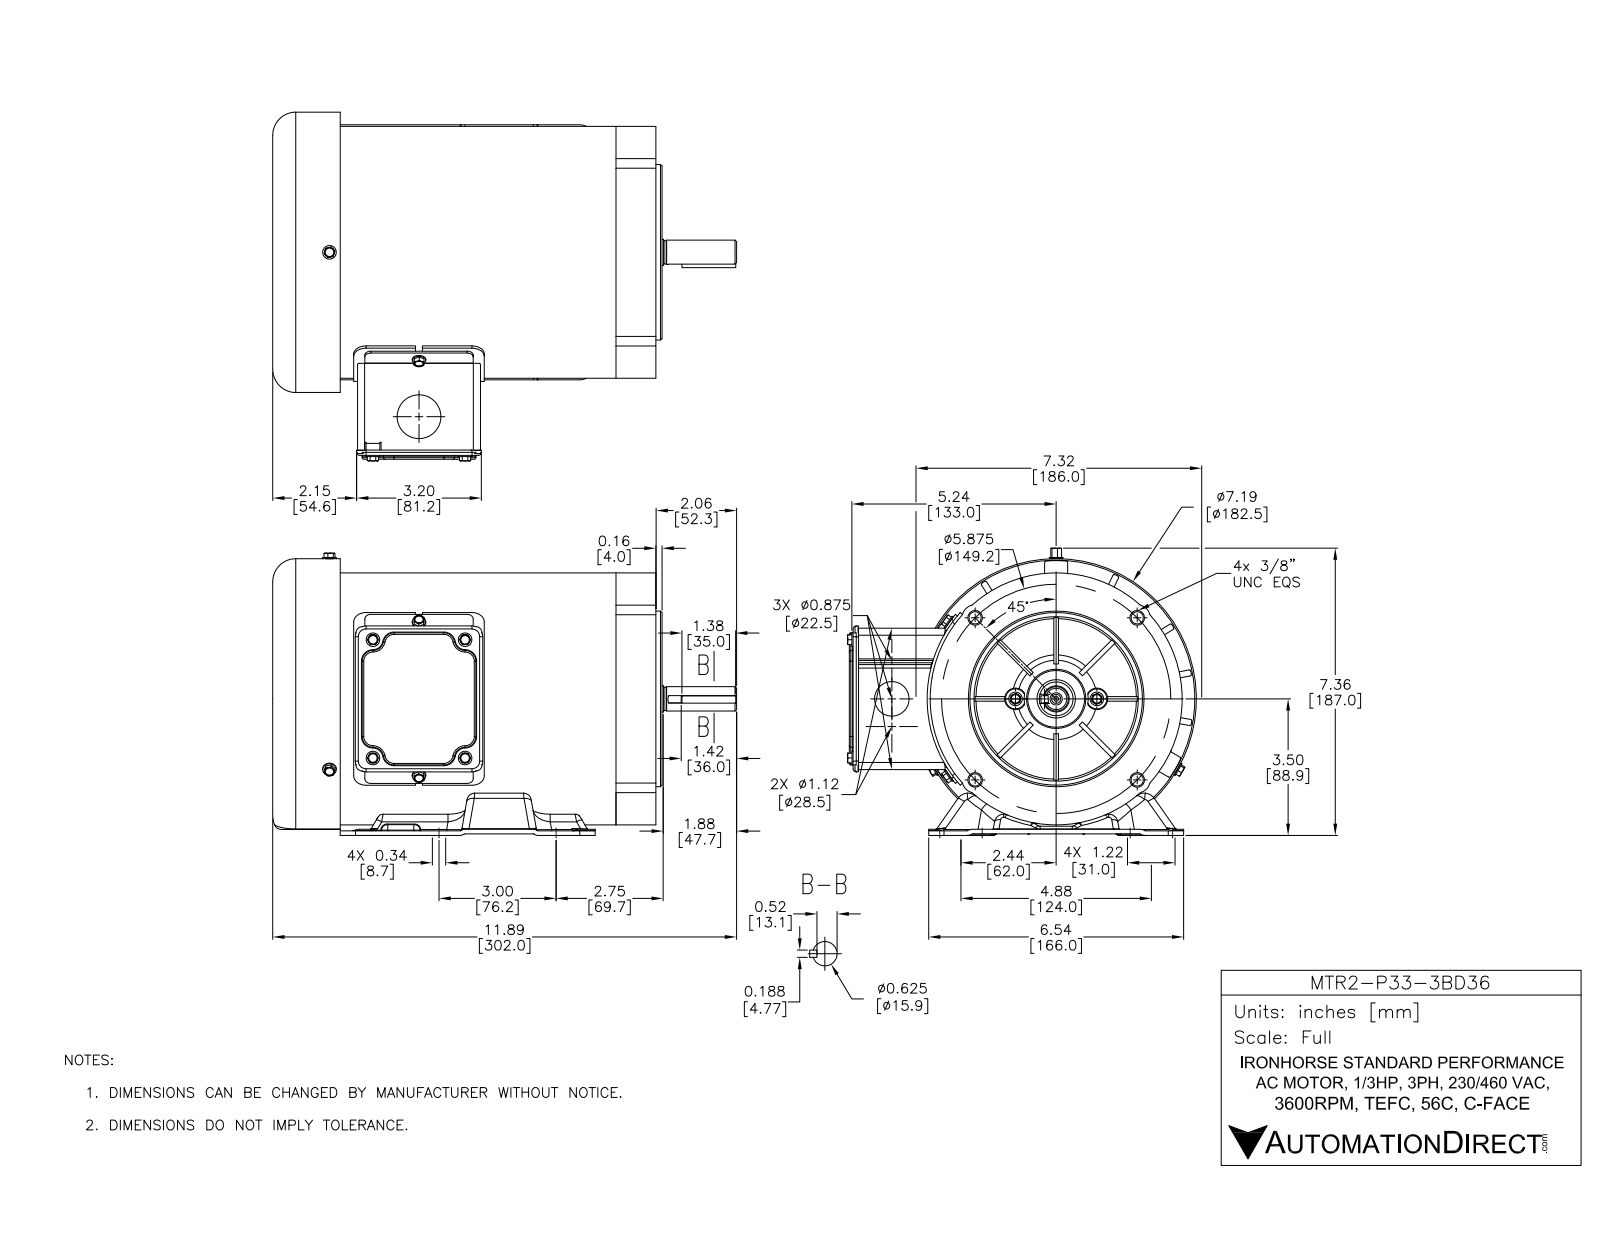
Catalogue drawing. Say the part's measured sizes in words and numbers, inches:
The part is named "MTR2-P33-3BD36". Its 3-D file was written by "SolidWorks 2016 (AUTOMOTIVE_DESIGN)". It is 37 solids with 2761 faces: 763 planar, 888 cylindrical and 1110 other. Overall it measures 11.634 by 8.938 by 7.234 inches. Its volume is 48.55 cubic inches and its surface area 976.3 square inches. Round holes: 12 of diameter 0.197, 11 of diameter 0.219, 8 of diameter 0.276, 6 of diameter 0.217, 6 of diameter 0.344, 5 of diameter 0.136, 4 of diameter 0.15, 4 of diameter 0.177, 4 of diameter 0.313, 2 of diameter 0.067, 2 of diameter 0.134, 2 of diameter 0.512. Round bosses or shafts: 11 of diameter 0.164, 7 of diameter 0.348, 6 of diameter 0.25, 4 of diameter 0.348, 1 of diameter 7.185, 1 of diameter 6.457, 1 of diameter 4.5, 1 of diameter 0.945. Partial cylindrical surfaces (rounded edges, fillets, slot ends): 121 of radius 0.118, 38 of radius 0.039, 32 of radius 0.02, 32 of radius 0.157, 26 of radius 0.138, 19 of radius 0.276, 12 of radius 0.172, 12 of radius 0.197. The main face-to-face distances are 0.118, 0.039, 0.063, 8.386, 1.024, 1.142, 9.528, 9.567, 3.559, 0.079. The hole center spacings are 4.221, 3.031, 0.094, 2.32, 2.409, 2.937, 2.979, 3.748.
